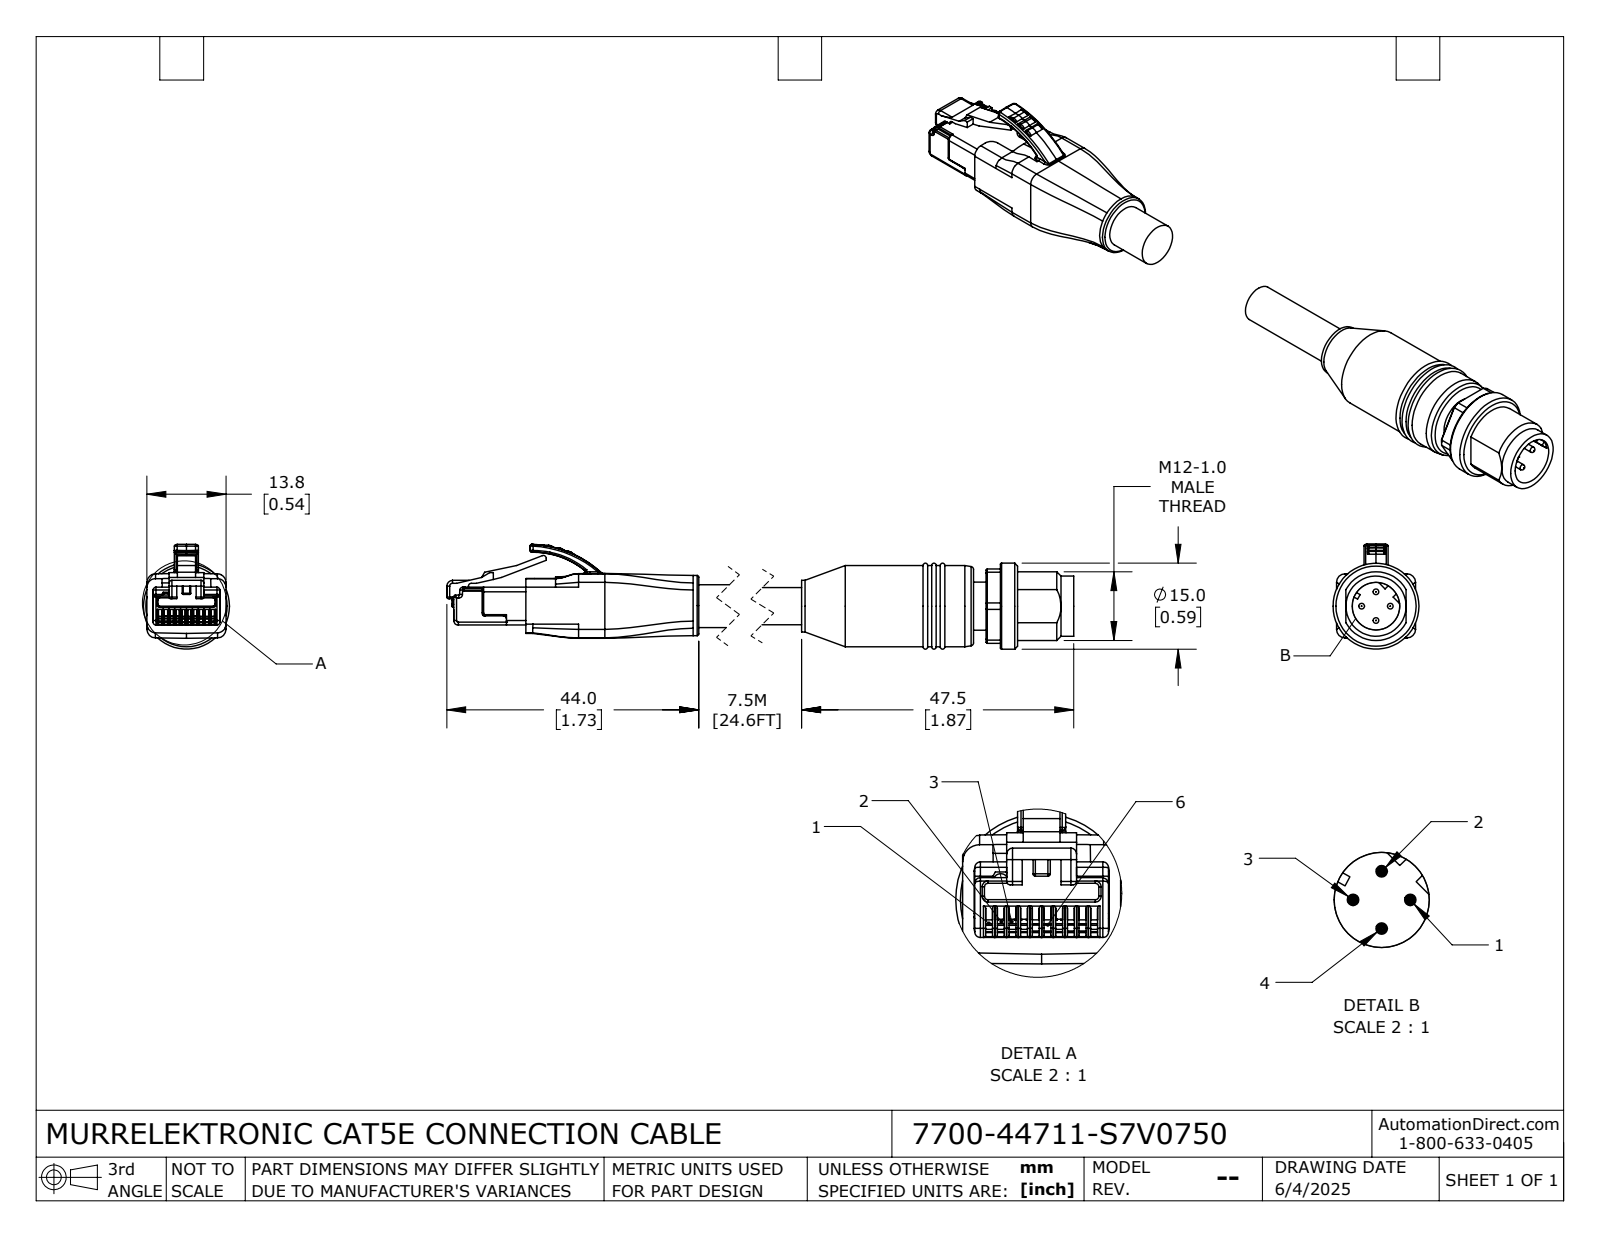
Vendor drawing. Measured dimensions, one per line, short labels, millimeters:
name: 7700-44711-S7V0750_MALE; 7700-44711-S7V0750; 7700-44711-S7V0750_RJ45
written by: SolidWorks 2024 (CONFIG_CONTROL_DESIGN)
unit: mm
bodies: 2 solids, 757 faces (357 planar, 235 cylindrical, 165 other)
size: 144.5 × 18.29 × 15
volume: 11 873 mm³; area: 5 775 mm²
holes: 1× ⌀8.3
bosses: 4× ⌀1, 2× ⌀10.5, 1× ⌀15, 1× ⌀14.2, 1× ⌀9, 1× ⌀8.4, 1× ⌀7.5, 1× ⌀6.5
rounds: 61× R0.2, 25× R0.5, 14× R0.3, 9× R1.5, 5× R0.8, 2× R0.54, 2× R5, 1× R0.13
face distances: 13.8, 2.2, 1.65, 12.15, 1.01, 12.79, 0.64, 11.14, 9.8, 0.9
